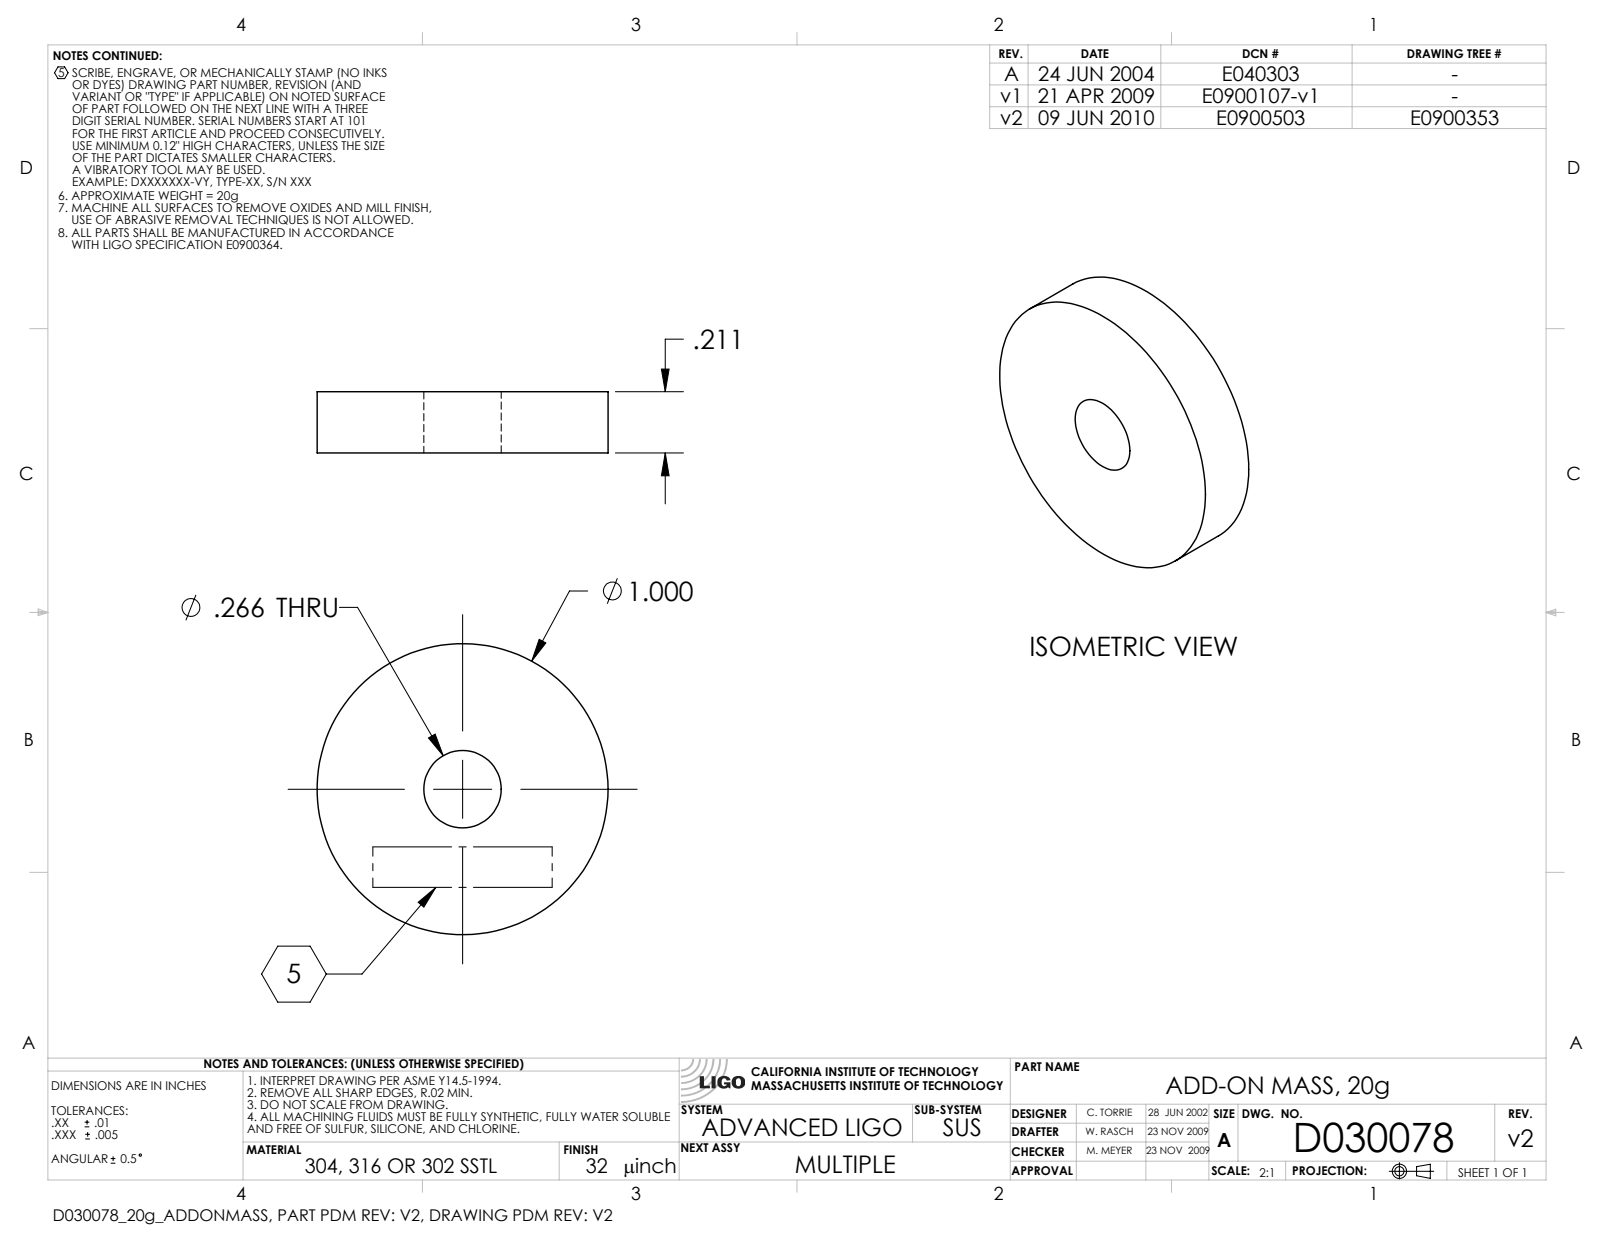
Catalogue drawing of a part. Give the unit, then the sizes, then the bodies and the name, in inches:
Units: inches
Overall size (bounding box): 1 × 1 × 0.211
Round holes (diameter × count): ⌀0.266 ×1
Round bosses / shafts (diameter × count): ⌀1 ×1
Main face-to-face distances: 0.211
Volume: 0.154 in³ · Surface area: 2.297 in²
Bodies: 1 solid, 6 faces (2 planar, 4 cylindrical, 0 other)
Part name (STEP PRODUCT): D030078-v2_aLIGO_SUS_HSTS_20g Addon Mass
STEP written by: SolidWorks 2009 (CONFIG_CONTROL_DESIGN)
